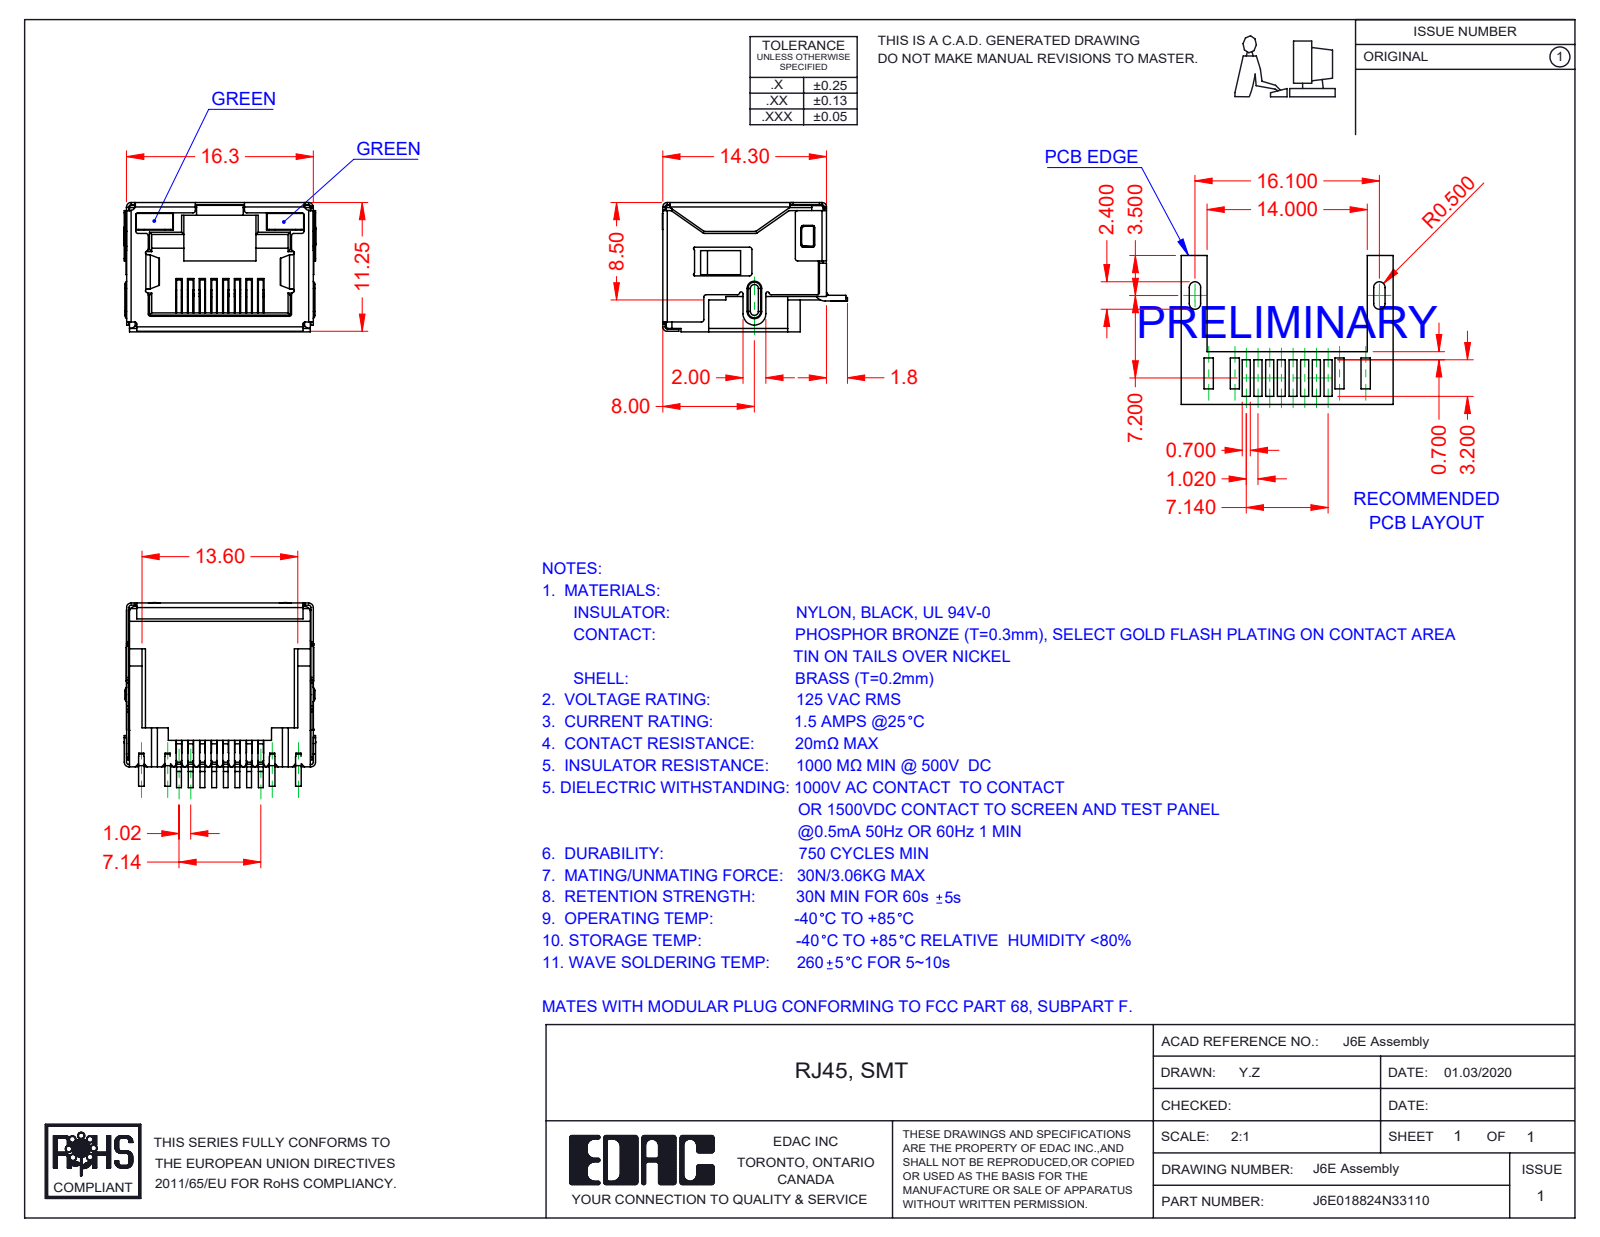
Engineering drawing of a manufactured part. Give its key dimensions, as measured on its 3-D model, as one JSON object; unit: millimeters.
{"part_name": "J6E018824N33110; 6E Contacts; 6E Insulator_LED; 6E LED LH_3-Green (+2 more)", "step_written_by": "SolidWorks 2016 (CONFIG_CONTROL_DESIGN)", "units": "millimeters", "bodies": {"solids": 12, "faces": 1496, "planar": 1099, "cylindrical": 347, "other": 50}, "overall_size": [16.75, 16.15, 11.3], "volume_mm3": 1109, "surface_area_mm2": 4045, "partial_cylinders_radius": [[0.2, 82], [0.25, 17], [0.4, 13], [0.5, 13], [0.1, 10], [0.15, 7], [0.3, 4], [1, 3]], "face_to_face_distances": [11.05, 16.05, 16.1, 15.85, 11.1, 11.3, 2.4, 0.7, 9.85, 0.49]}
